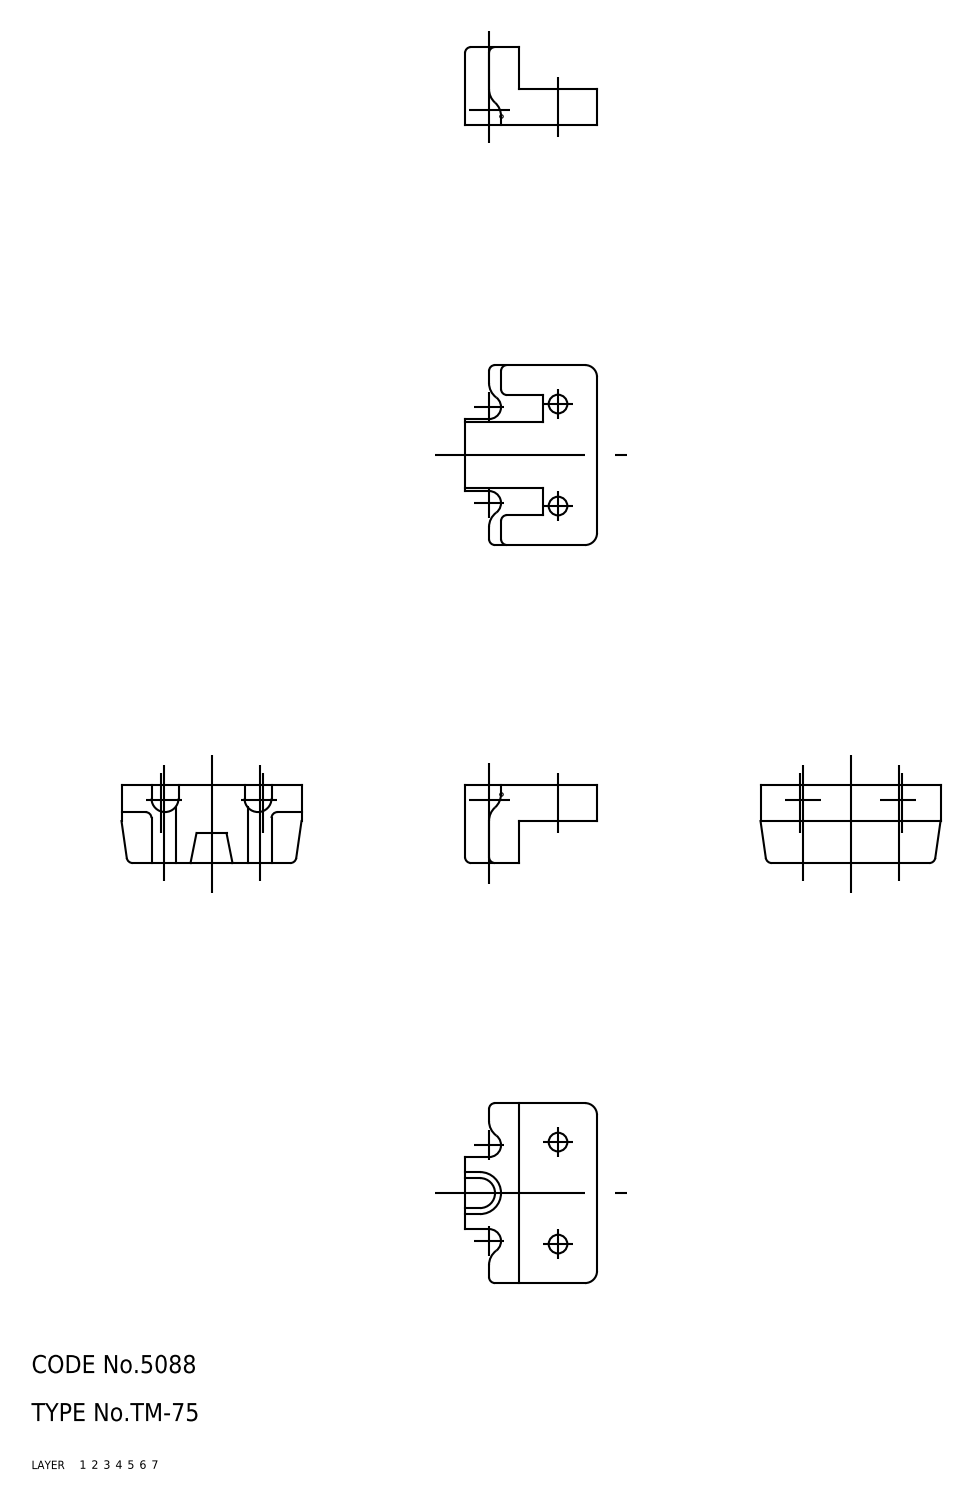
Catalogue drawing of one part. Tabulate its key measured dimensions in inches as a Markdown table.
| quantity | value |
| --- | --- |
| part name | holder |
| STEP written by | CADfix (AUTOMOTIVE_DESIGN) |
| units | inches |
| bodies | 1 solid, 80 faces (0 planar, 0 cylindrical, 80 other) |
| overall size | 1.181 × 0.866 × 0.512 |
| volume | 0.25 in³ |
| surface area | 3.875 in² |
